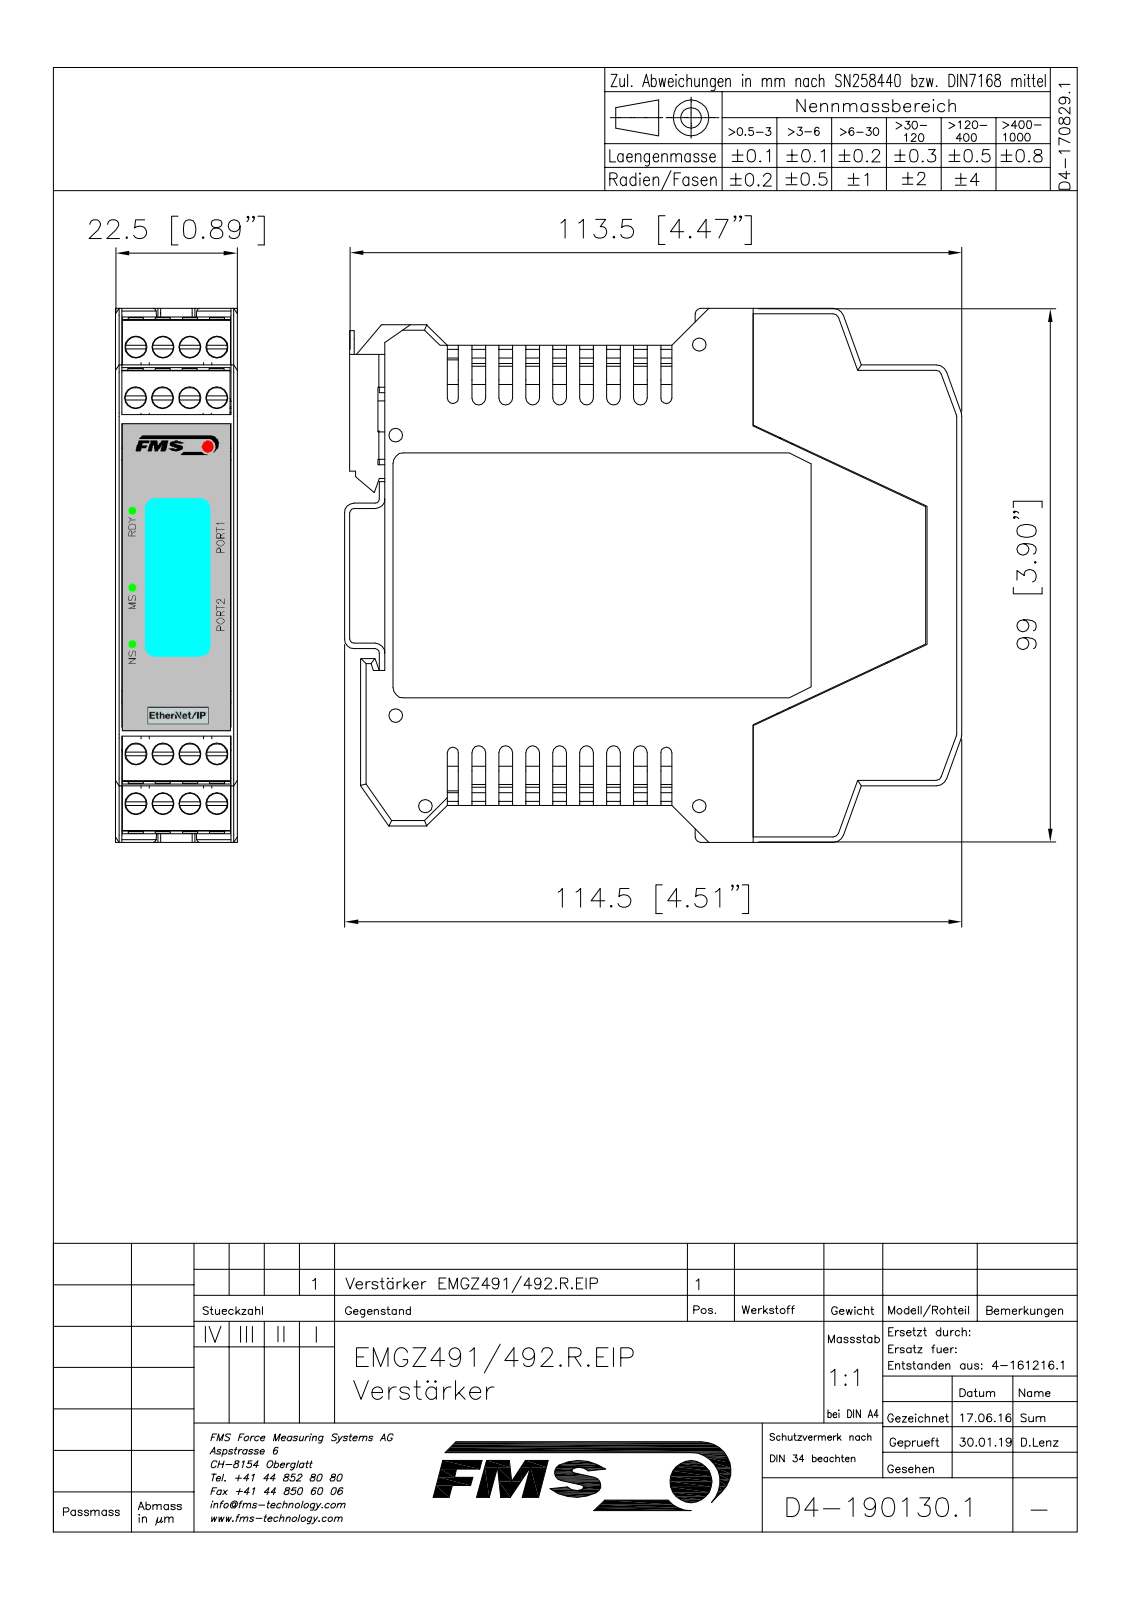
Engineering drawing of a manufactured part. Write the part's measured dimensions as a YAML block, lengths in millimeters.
part_name: "E1901301_STP; 0073F3XX00; E1605272; 0073B01400 (+8 more)"
step_written_by: "Mechanical Desktop 2009 (CONFIG_CONTROL_DESIGN)"
units: millimeters
bodies: {solids: 39, faces: 2665, planar: 1806, cylindrical: 651, other: 208}
overall_size: [113.5, 99, 22.5]
volume: 53531
surface_area: 64654
round_holes:
  - {diameter: 3.85, count: 16}
  - {diameter: 4.05, count: 16}
  - {diameter: 1.6, count: 12}
  - {diameter: 2.5, count: 5}
  - {diameter: 1.5, count: 3}
round_bosses_or_shafts:
  - {diameter: 5, count: 1}
partial_cylinders:
  - {radius: 0.4, count: 56}
  - {radius: 0.5, count: 25}
  - {radius: 0.1, count: 24}
  - {radius: 0.15, count: 24}
  - {radius: 2, count: 24}
  - {radius: 0.2, count: 21}
  - {radius: 1, count: 14}
  - {radius: 1.25, count: 14}
face_to_face_distances: [21, 1.2, 1.5, 22.2, 20.7, 19.5, 22.5, 21.3, 0.9, 19.8]
hole_center_spacings: [5, 10, 15, 10.47, 19.16, 66.26, 75.67, 84.85]
